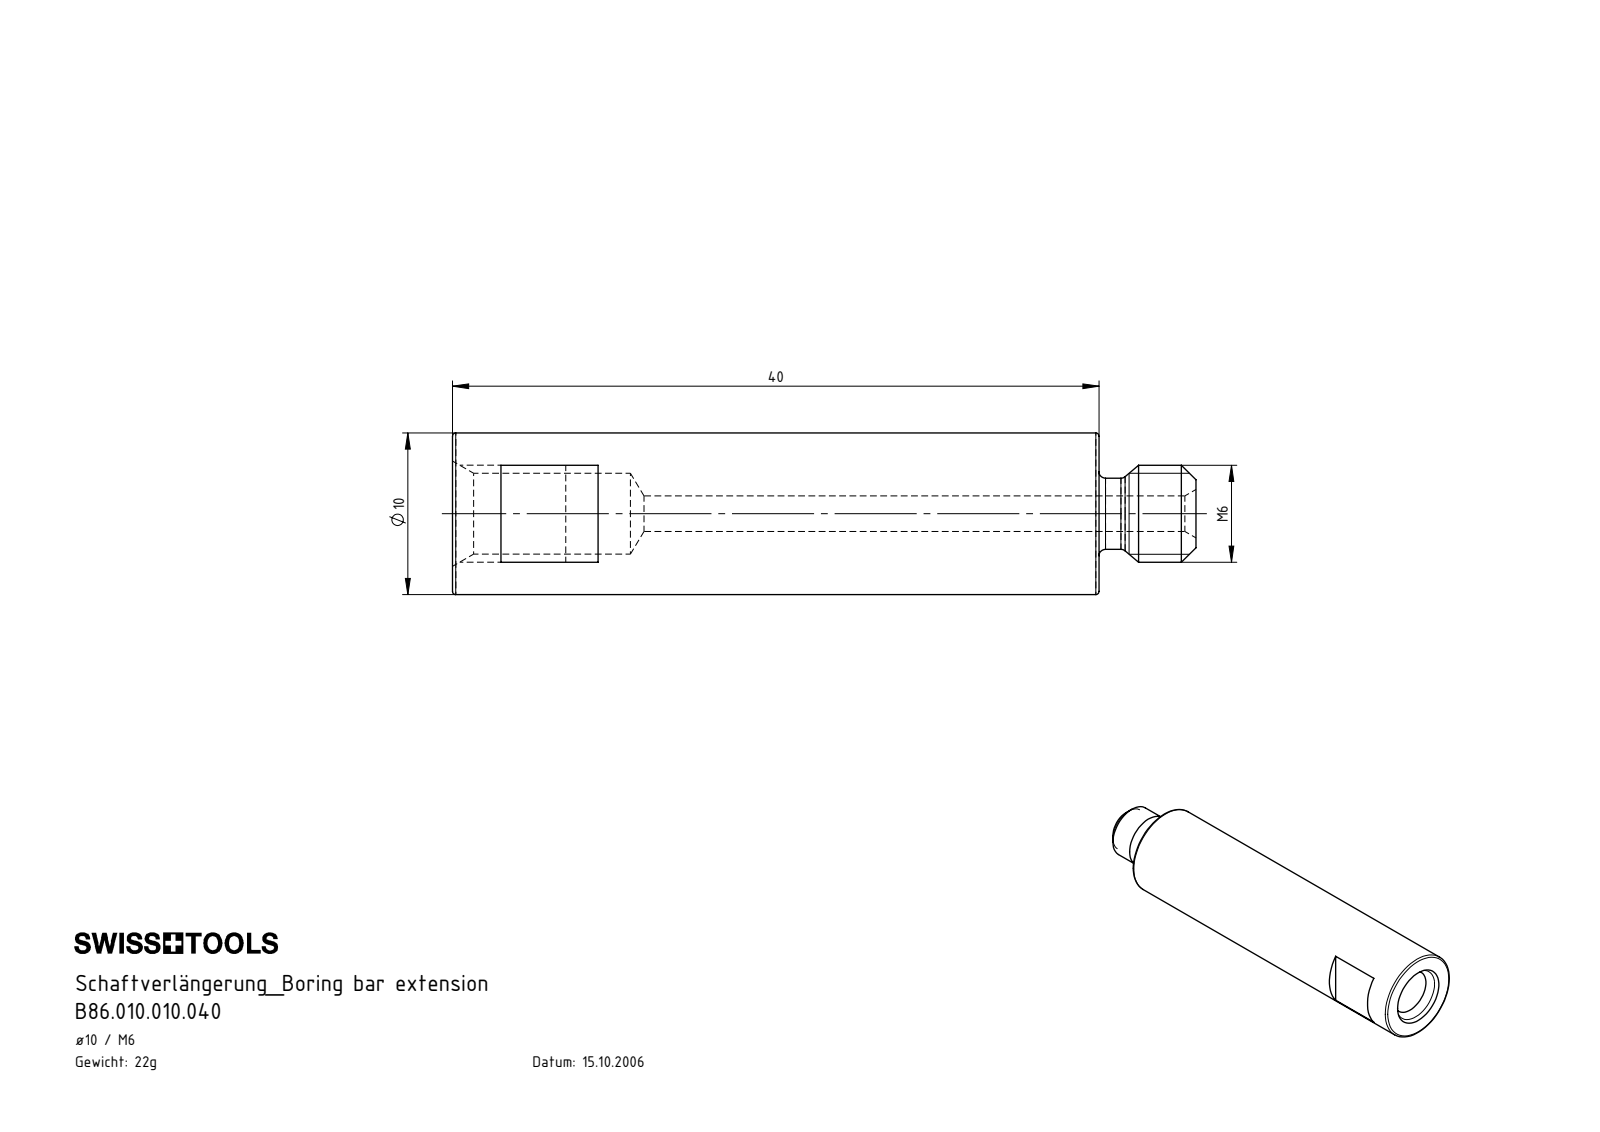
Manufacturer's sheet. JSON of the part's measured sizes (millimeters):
{"part_name": "B86.010.010.040", "step_written_by": "SolidWorks 2022 (CONFIG_CONTROL_DESIGN)", "units": "millimeters", "bodies": {"solids": 1, "faces": 37, "planar": 9, "cylindrical": 10, "other": 18}, "overall_size": [46, 10, 10], "volume_mm3": 2865, "surface_area_mm2": 1922, "round_holes": [[2.2, 1], [5, 1]], "round_bosses_or_shafts": [[10, 1], [6, 1], [4.4, 1]], "face_to_face_distances": [40, 8, 37, 6, 3, 31, 9, 43, 46]}
